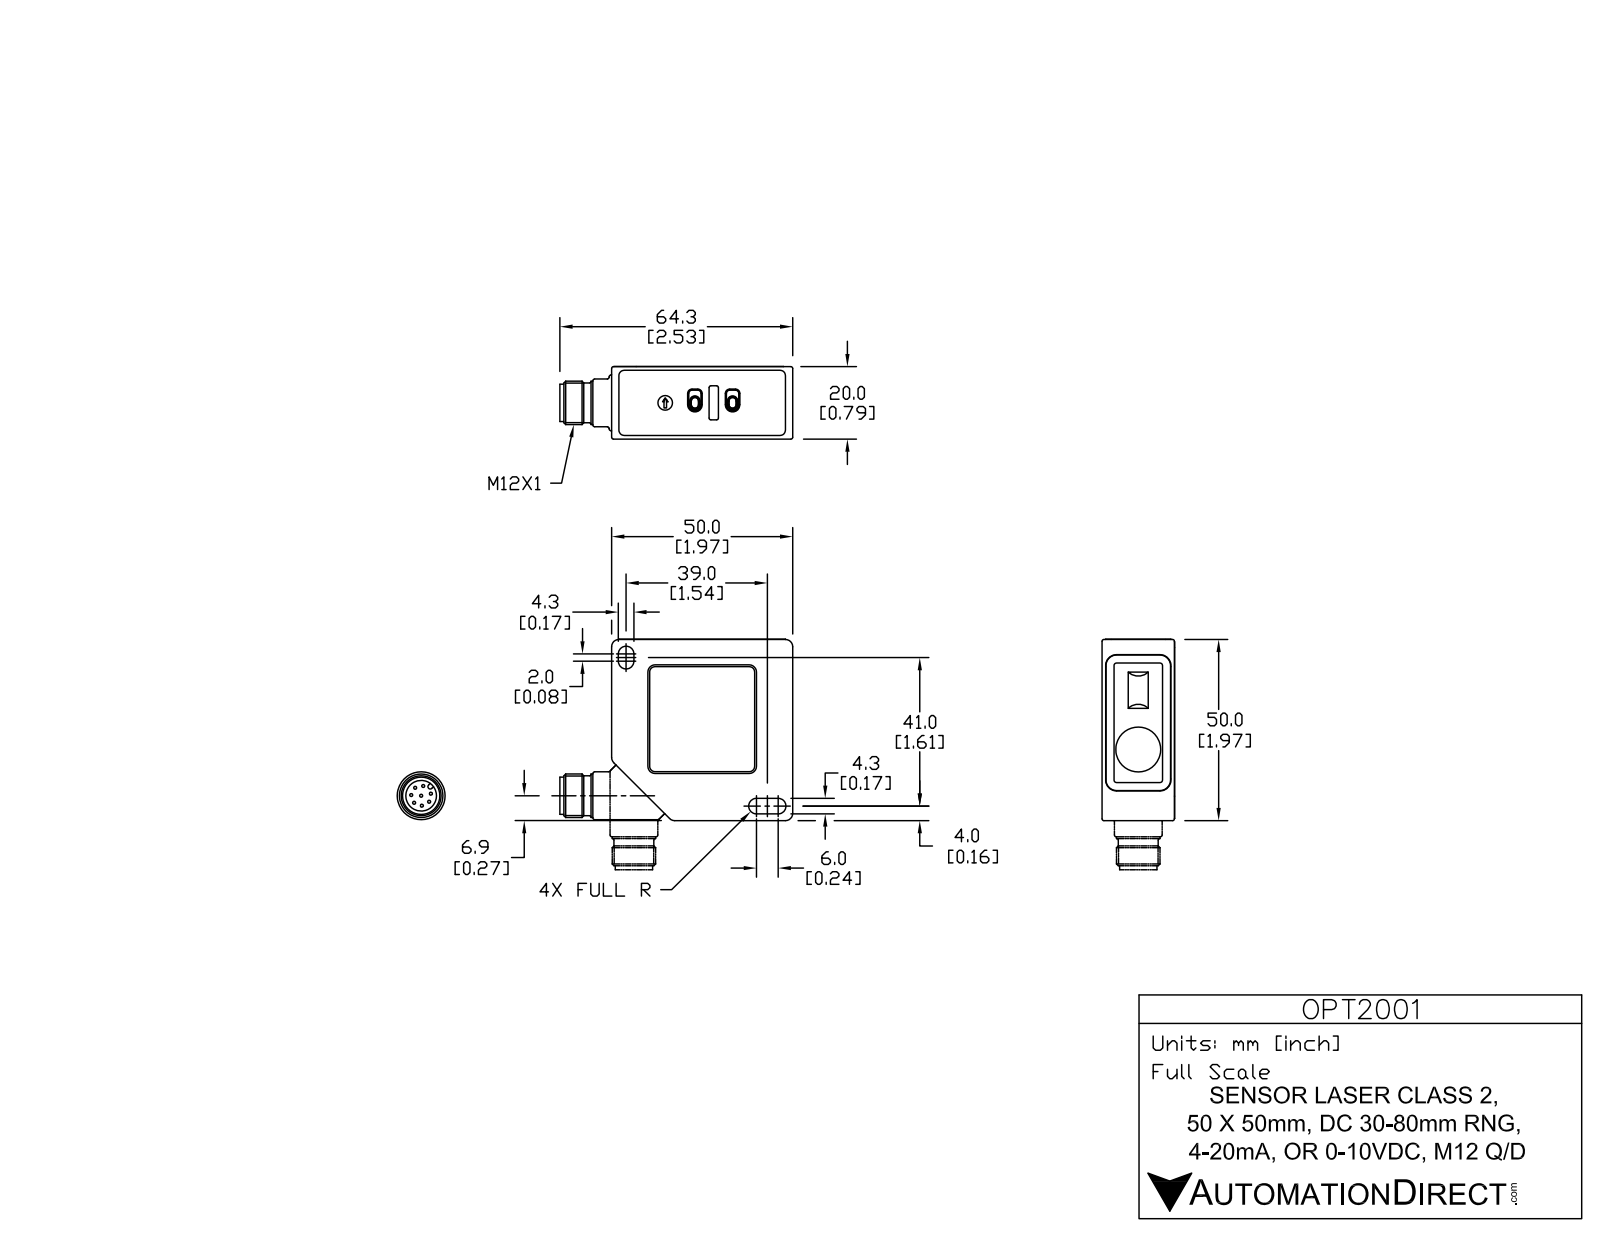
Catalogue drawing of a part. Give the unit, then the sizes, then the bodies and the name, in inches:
Units: inches
Overall size (bounding box): 2.537 × 1.972 × 0.787
Round holes (diameter × count): ⌀0.157 ×1, ⌀0.333 ×1
Round bosses / shafts (diameter × count): ⌀0.032 ×8, ⌀0.709 ×1, ⌀0.531 ×1, ⌀0.488 ×1, ⌀0.472 ×1, ⌀0.433 ×1, ⌀0.406 ×1
Partial cylindrical surfaces — rounded edges, fillets, slot ends (radius × count): R0.079 ×17, R0.008 ×10, R0.039 ×8, R0.083 ×5, R0.02 ×4, R0.047 ×4, R0.085 ×4, R0.114 ×4
Main face-to-face distances: 0.787, 0.78, 1.969, 1.972, 1.902, 0.063, 1.906, 0.21, 2.111, 2.115
Volume: 2.969 in³ · Surface area: 24.84 in²
Bodies: 15 solids, 301 faces (153 planar, 134 cylindrical, 14 other)
Part name (STEP PRODUCT): OPT2001
STEP written by: SolidWorks 2013 (AUTOMOTIVE_DESIGN)
